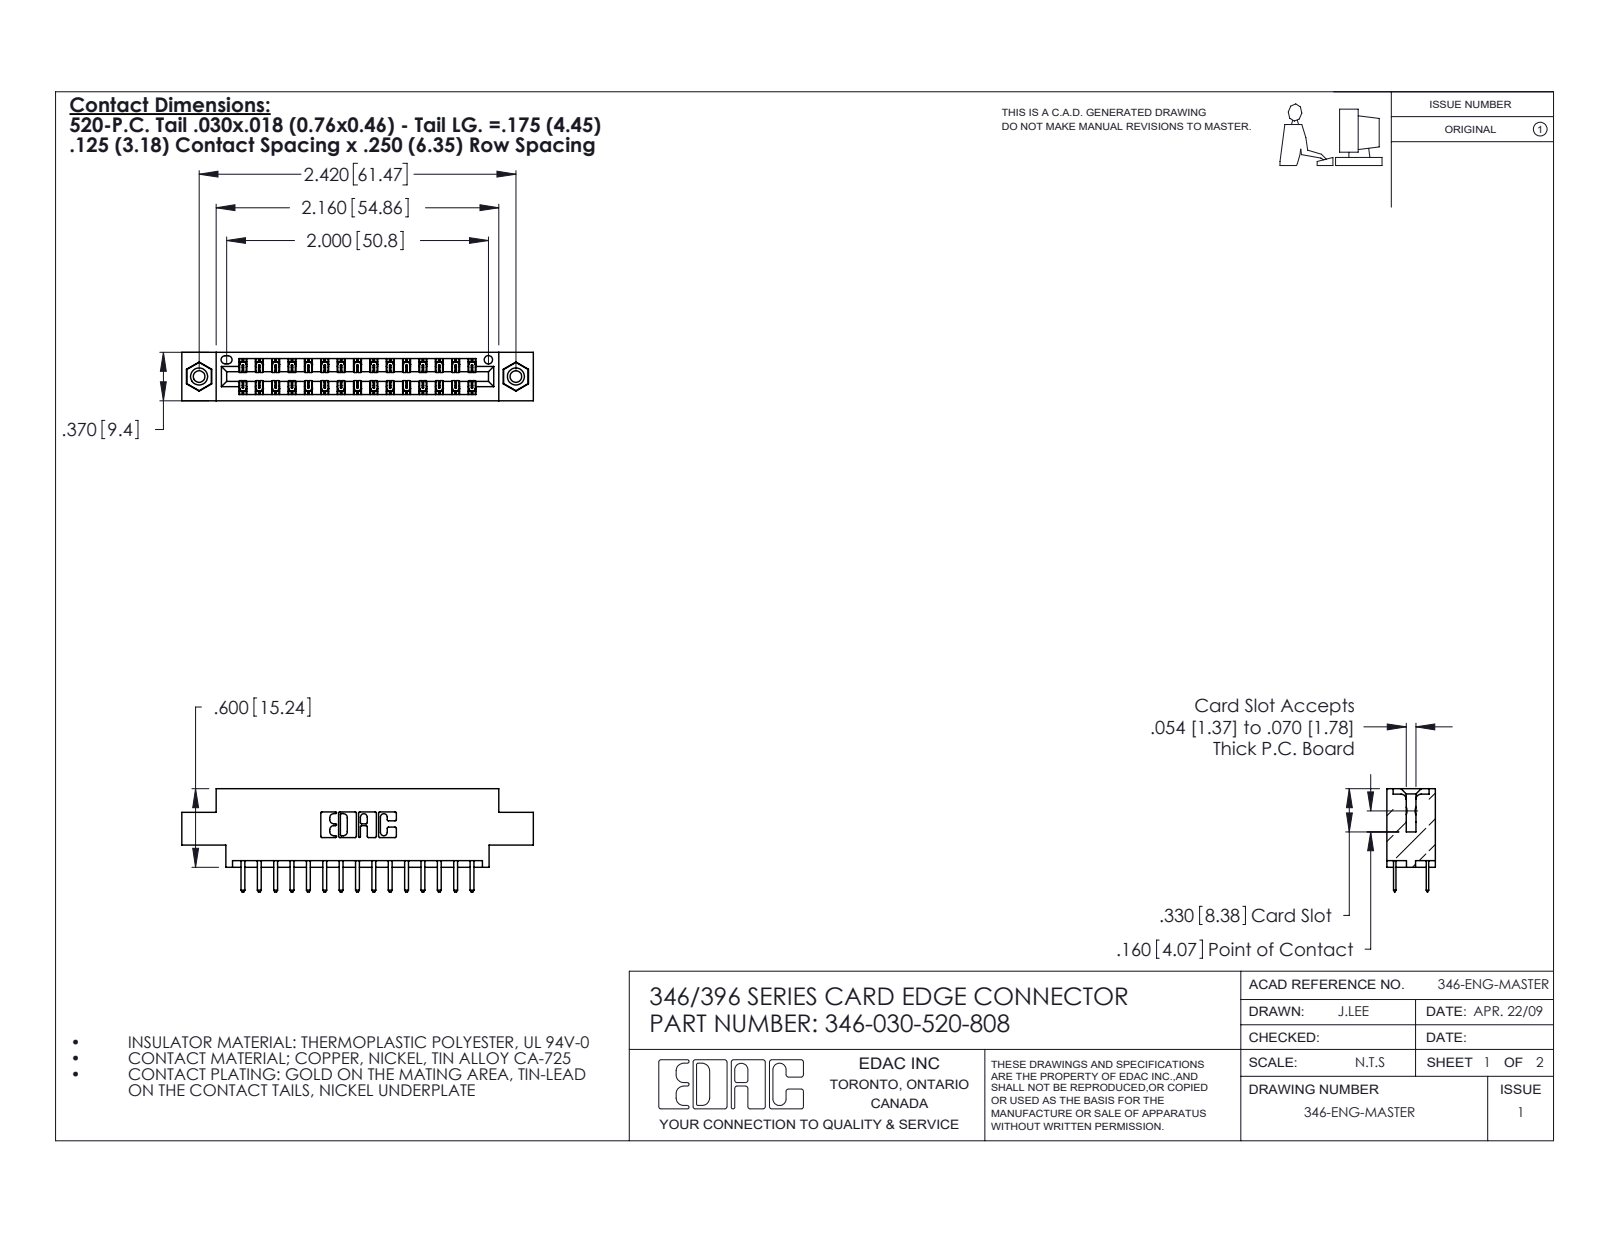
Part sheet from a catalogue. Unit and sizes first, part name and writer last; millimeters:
Units: millimetres
Overall size (bounding box): 68.2 × 20 × 9.4
Round holes (diameter × count): ⌀2.3 ×2, ⌀3.2 ×2, ⌀4 ×2, ⌀1.6 ×1
Round bosses / shafts (diameter × count): ⌀3.9 ×2
Partial cylindrical surfaces — rounded edges, fillets, slot ends (radius × count): R0.2 ×45, R0.3 ×34, R0.3 ×22, R0.2 ×6, R0.8 ×6, R0.7 ×3, R0.4 ×2, R0.6 ×2
Main face-to-face distances: 6.4, 1.2, 8.2, 9.4, 5.6, 3.8, 7, 1.8, 7.6, 0.6
Hole centre spacings: 6.2, 56.2, 61.5
Volume: 6 260 mm³ · Surface area: 8 355 mm²
Bodies: 33 solids, 1866 faces (1222 planar, 628 cylindrical, 16 other)
Part name (STEP PRODUCT): 345-292-001_345-293-120; 346-030-520-808; 346 Part_0.170 Offset - 0.156 Dia-TI; 345-250-001_345-250-003-102
STEP written by: SolidWorks 2020 (CONFIG_CONTROL_DESIGN)
